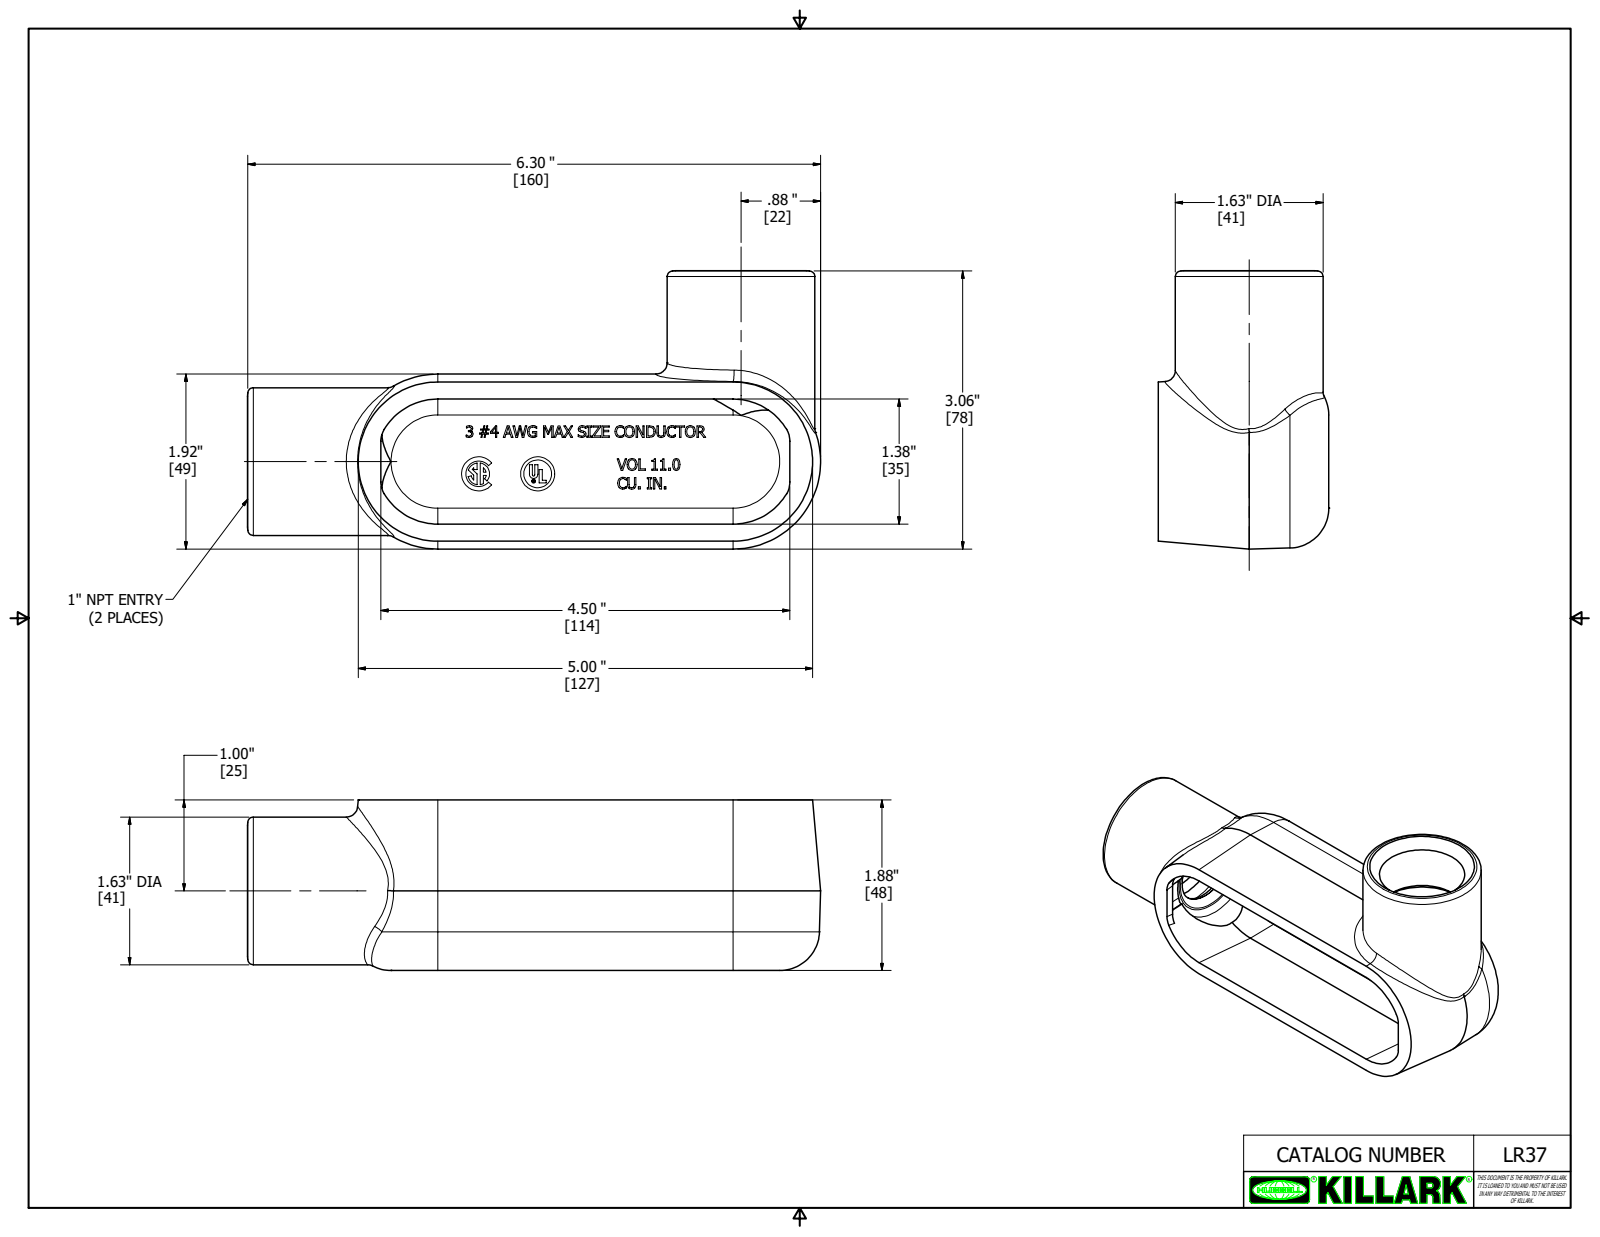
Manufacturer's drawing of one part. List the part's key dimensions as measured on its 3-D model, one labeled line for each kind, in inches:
Part name (STEP PRODUCT): 17671-2
STEP written by: Autodesk Inventor 2018 (AUTOMOTIVE_DESIGN)
Units: inches
Bodies: 1 solid, 828 faces (521 planar, 36 cylindrical, 271 other)
Overall size (bounding box): 6.306 × 3.061 × 1.875
Volume: 6.959 in³ · Surface area: 77.93 in²
Round holes (diameter × count): ⌀1.321 ×2, ⌀0.035 ×1, ⌀0.306 ×1, ⌀1.375 ×1
Round bosses / shafts (diameter × count): ⌀1.625 ×2, ⌀0.375 ×1, ⌀0.042 ×1
Partial cylindrical surfaces — rounded edges, fillets, slot ends (radius × count): R0.062 ×4, R0.125 ×4, R0.25 ×2, R0.437 ×2, R0.004 ×1, R0.007 ×1, R0.012 ×1, R0.047 ×1
Main face-to-face distances: 0.187, 0.187, 0.188, 1.875, 1.687, 0.031, 0.156, 1.844, 0.219, 1.656
Hole centre spacings: 0.092
